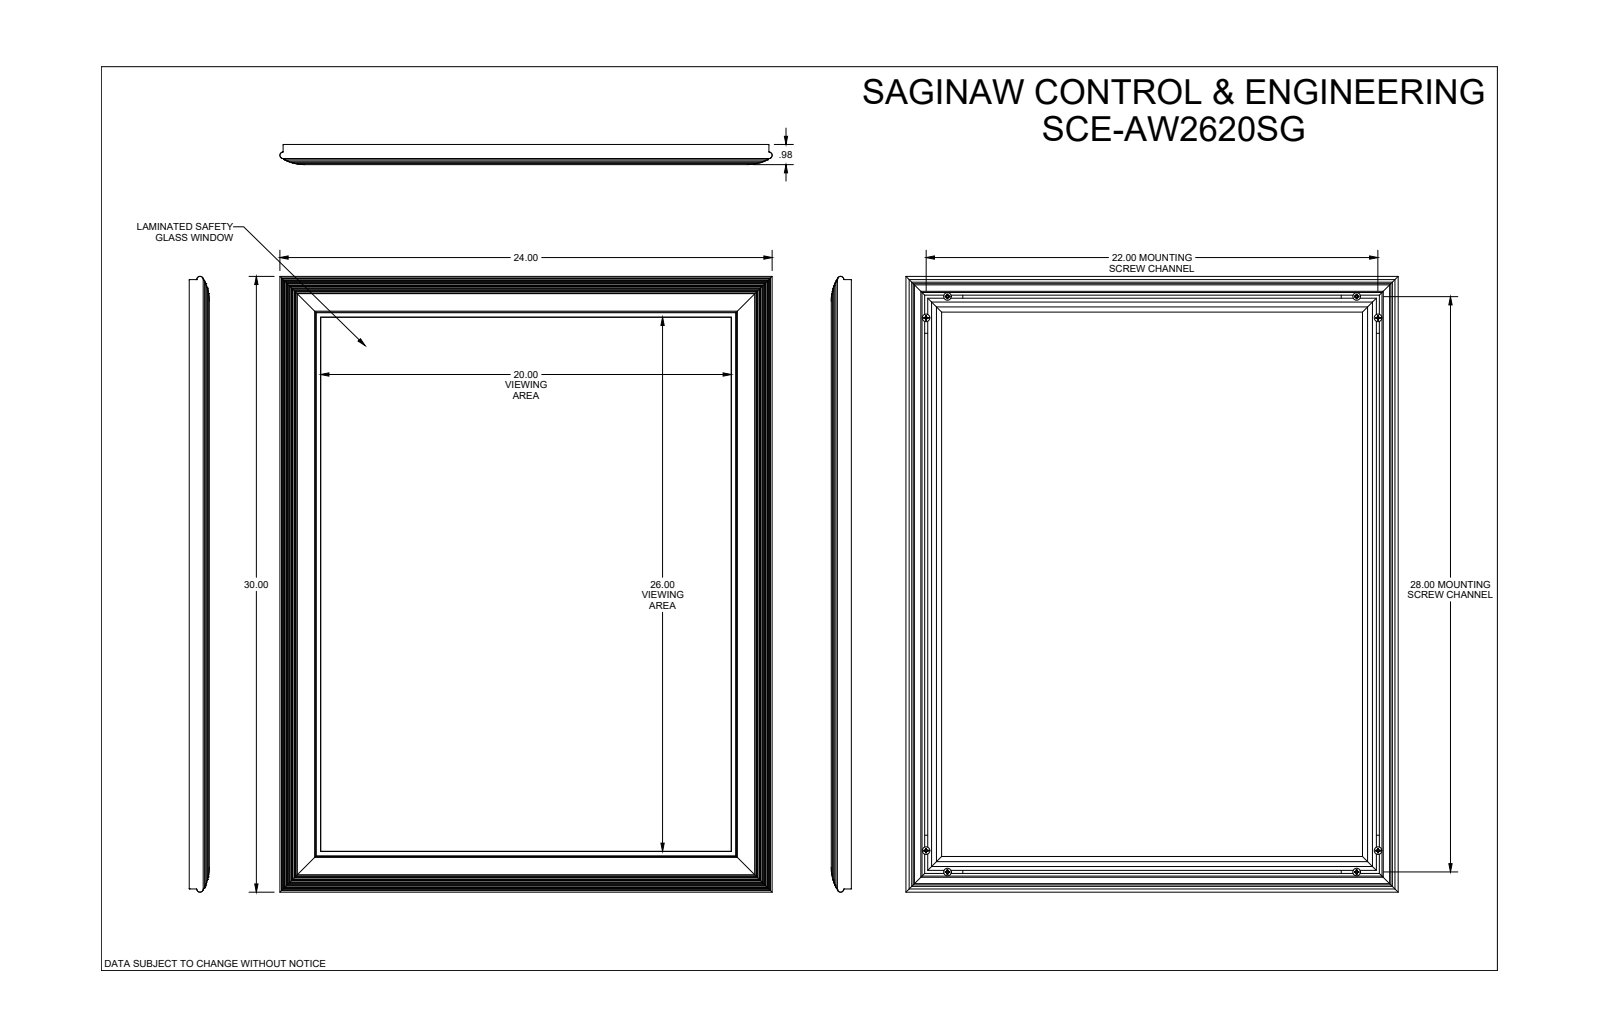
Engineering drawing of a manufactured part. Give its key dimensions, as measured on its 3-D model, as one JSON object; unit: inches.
{"part_name": "SCE-AW2620SG", "step_written_by": "SolidWorks 2019 (CONFIG_CONTROL_DESIGN)", "units": "inches", "bodies": {"solids": 25, "faces": 1202, "planar": 454, "cylindrical": 308, "other": 440}, "overall_size": [29.976, 23.976, 0.98], "volume_in3": 190.6, "surface_area_in2": 2602, "round_holes": [[0.148, 8], [0.165, 4]], "round_bosses_or_shafts": [[0.19, 8], [0.122, 8]], "partial_cylinders_radius": [[0.02, 156], [0.059, 24], [0.01, 16], [0.03, 12], [0.016, 4], [0.02, 4], [0.06, 4], [0.157, 4]], "face_to_face_distances": [0.236, 0.06, 0.065, 0.075, 0.216, 0.02, 1.52, 0.563, 0.125, 0.313], "hole_center_spacings": [1.474, 20.999, 26.994, 34.168, 19.931, 22.016, 25.931, 28.016]}
